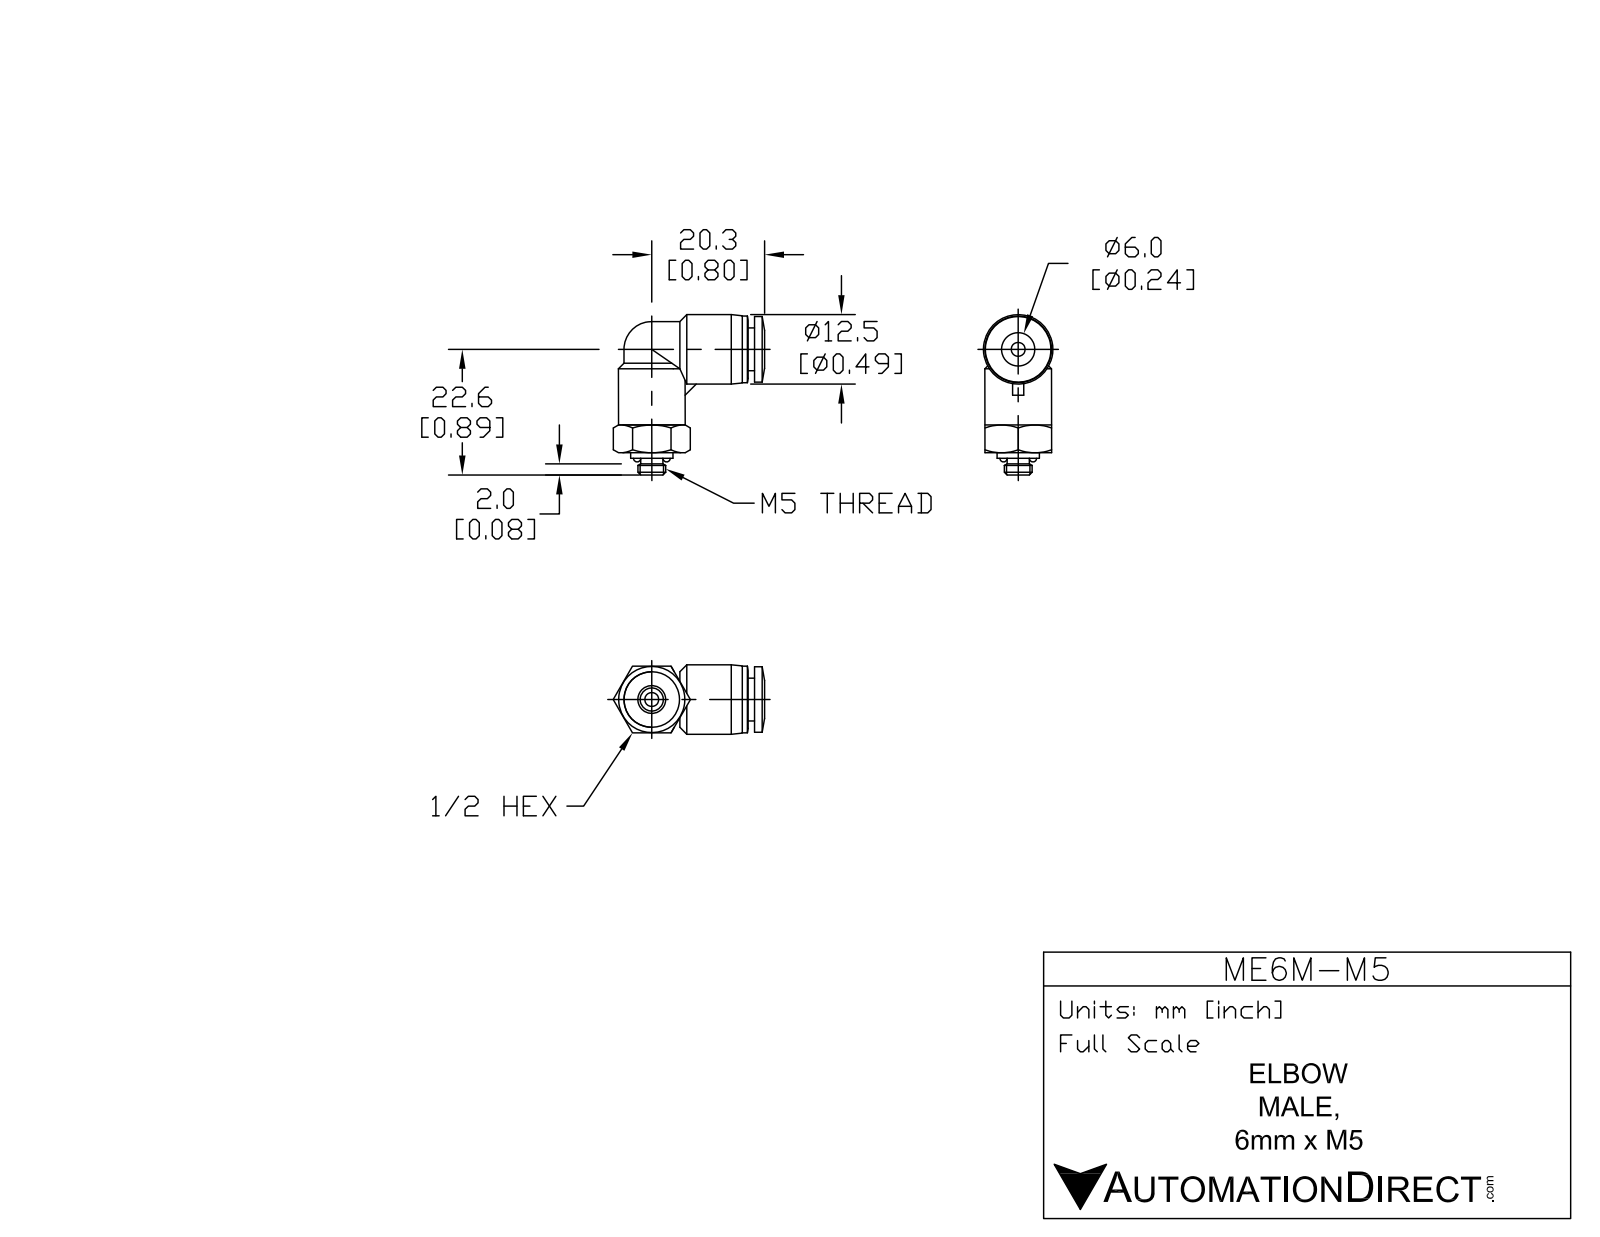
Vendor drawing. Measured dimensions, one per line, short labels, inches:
name: ME6M-M5
written by: SolidWorks 2015 (AUTOMOTIVE_DESIGN)
unit: in
bodies: 2 solids, 87 faces (19 planar, 27 cylindrical, 41 other)
size: 1.132 × 1.072 × 0.492
volume: 0.21 in³; area: 3.75 in²
holes: 2× ⌀0.098, 1× ⌀0.248
bosses: 2× ⌀0.472, 1× ⌀0.492, 1× ⌀0.465, 1× ⌀0.303, 1× ⌀0.299, 1× ⌀0.197, 1× ⌀0.157
rounds: 2× R0.197
face distances: 0.472, 0.045, 0.53, 0.575, 0.197, 0.157, 0.189, 0.031, 0.039, 0.276
